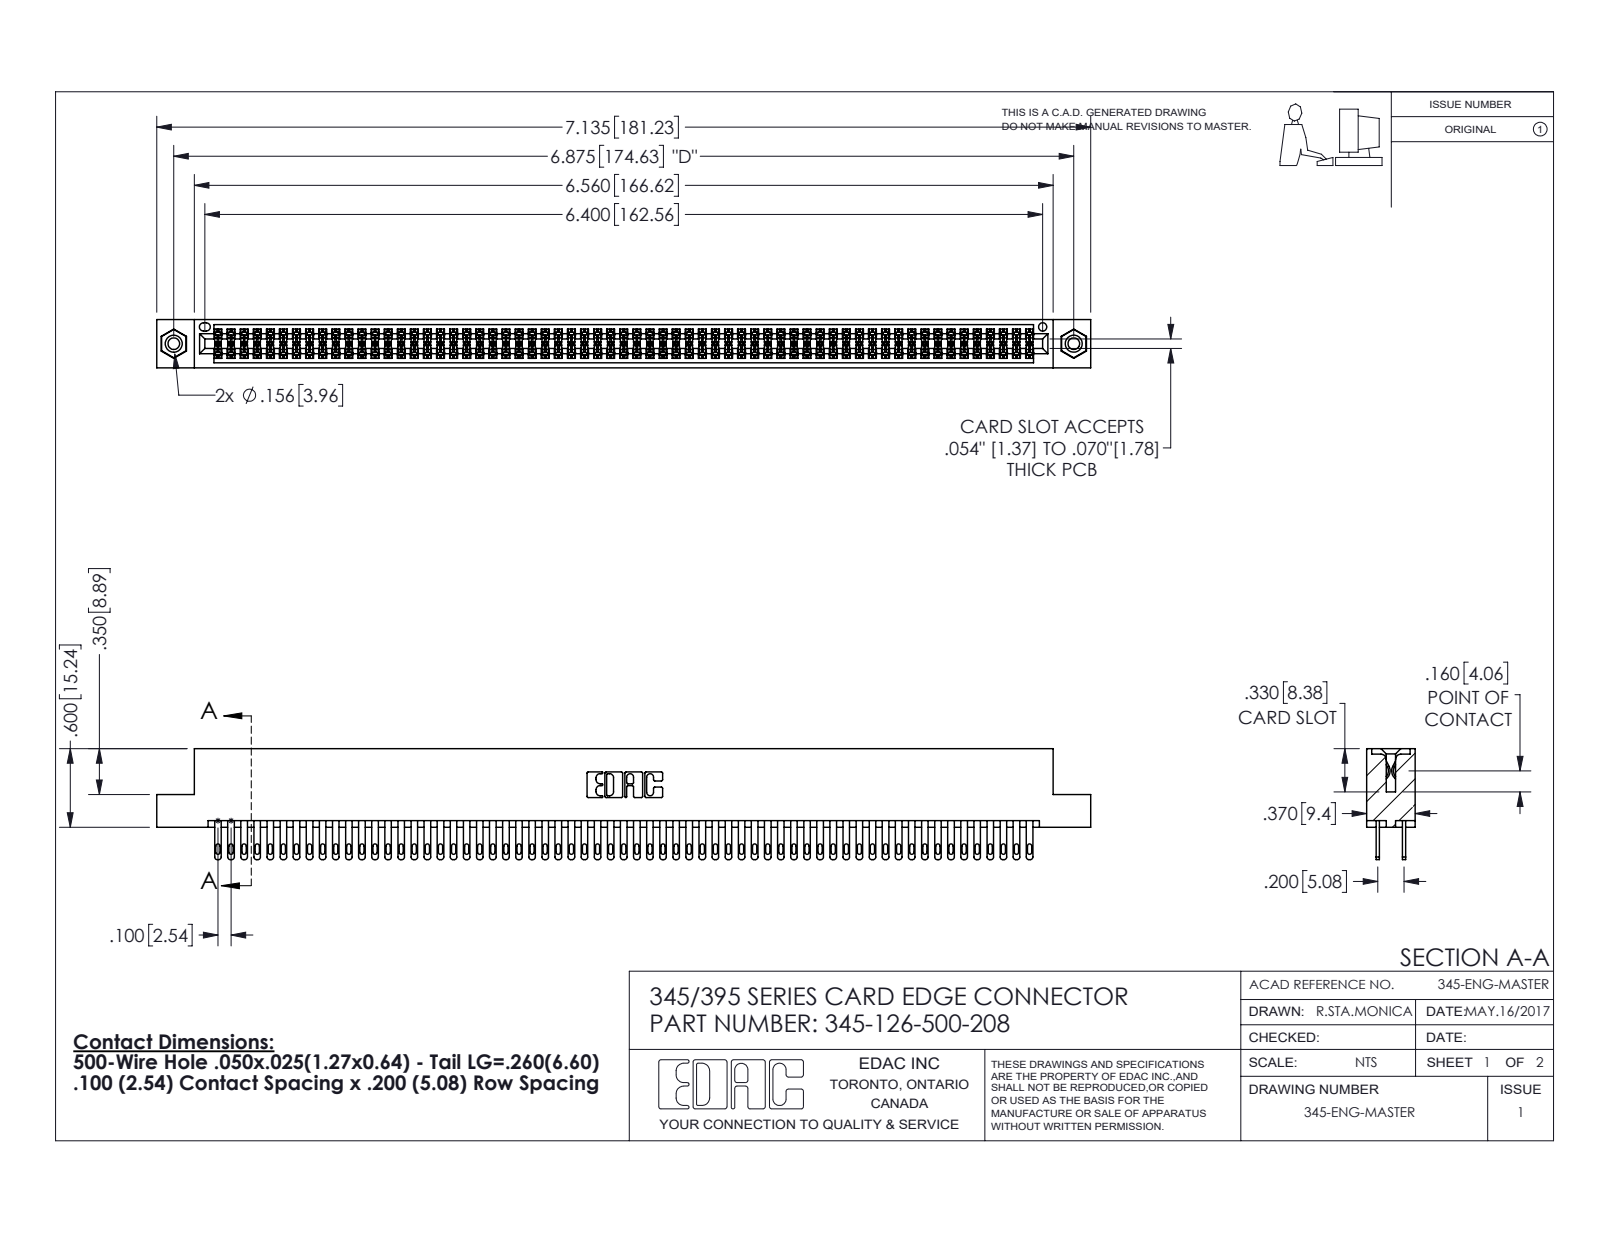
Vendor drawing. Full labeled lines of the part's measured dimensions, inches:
Part name (STEP PRODUCT): 345-126-500-208; 345-292-001_345-293-100; 345 Part_Flush Mounting Lugs - 0.156 Dia-TI; 345-250-001_345-250-003-102
STEP written by: SolidWorks 2016 (CONFIG_CONTROL_DESIGN)
Units: inches
Bodies: 129 solids, 5982 faces (3514 planar, 2452 cylindrical, 16 other)
Overall size (bounding box): 7.135 × 0.847 × 0.37
Volume: 1.109 in³ · Surface area: 44.29 in²
Round holes (diameter × count): ⌀0.089 ×2, ⌀0.125 ×2, ⌀0.156 ×2, ⌀0.064 ×1
Round bosses / shafts (diameter × count): ⌀0.155 ×2
Partial cylindrical surfaces — rounded edges, fillets, slot ends (radius × count): R0.006 ×189, R0.016 ×126, R0.02 ×126, R0.01 ×22, R0.007 ×6, R0.031 ×6, R0.026 ×3, R0.014 ×2
Main face-to-face distances: 0.072, 0.298, 0.2, 0.098, 0.272, 0.025, 0.37, 0.225, 0.175, 0.149
Hole centre spacings: 0.27, 6.639, 6.875
